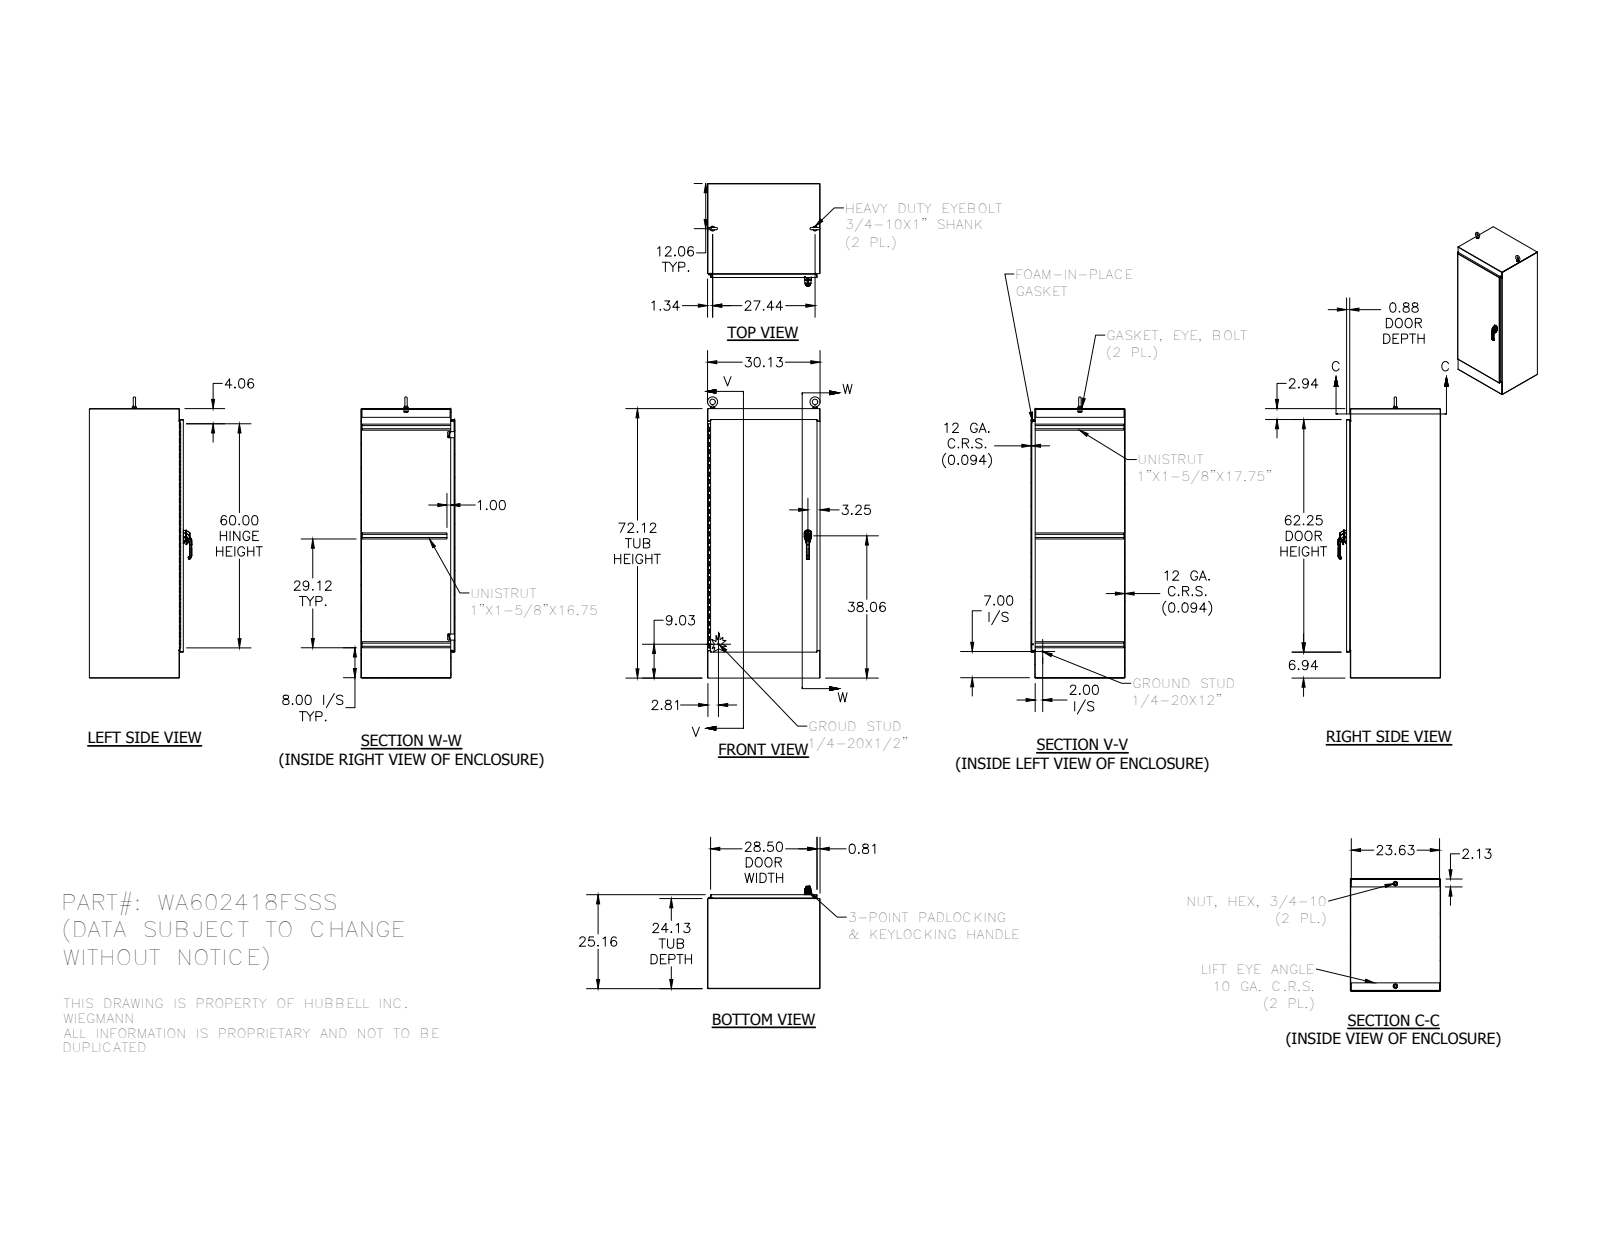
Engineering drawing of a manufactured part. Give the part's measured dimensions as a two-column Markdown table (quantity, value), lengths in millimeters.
| quantity | value |
| --- | --- |
| part name | WA723024FSBLS; WA7224FSRS; WA3024FSTOP; WA3024FSBTM (+8 more) |
| STEP written by | Autodesk Inventor 2014 (AUTOMOTIVE_DESIGN) |
| units | millimeters |
| bodies | 46 solids, 2855 faces (1212 planar, 995 cylindrical, 648 other) |
| overall size | 1911.29 × 765.17 × 696.2 |
| volume | 16 480 000 mm³ |
| surface area | 13 730 000 mm² |
| round holes (diameter × count) | 7.02 × 8, 5.08 × 4, 5.4 × 3, 7.11 × 3, 8 × 2, 10.2 × 2, 10.33 × 2, 10.5 × 2, 16.31 × 2, 20.64 × 2, 3.1 × 1, 3.15 × 1 |
| round bosses / shafts (diameter × count) | 6.35 × 3, 31.75 × 2, 28.45 × 2, 19.05 × 2, 13.5 × 2, 13.37 × 2, 11.05 × 2, 8.56 × 2 |
| partial cylindrical surfaces (radius × count) | 0.5 × 170, 0.3 × 101, 0.47 × 21, 0.25 × 16, 0.79 × 15, 2 × 14, 3.17 × 13, 0.48 × 12 |
| main face-to-face distances | 2.38, 636.7, 762.8, 760.42, 634.32, 639.08, 765.18, 1829.6, 610.4, 26.3 |
| hole center spacings | 9.66, 9.7, 9.71, 19.36, 19.4, 22.5, 29.06, 32.29 |
